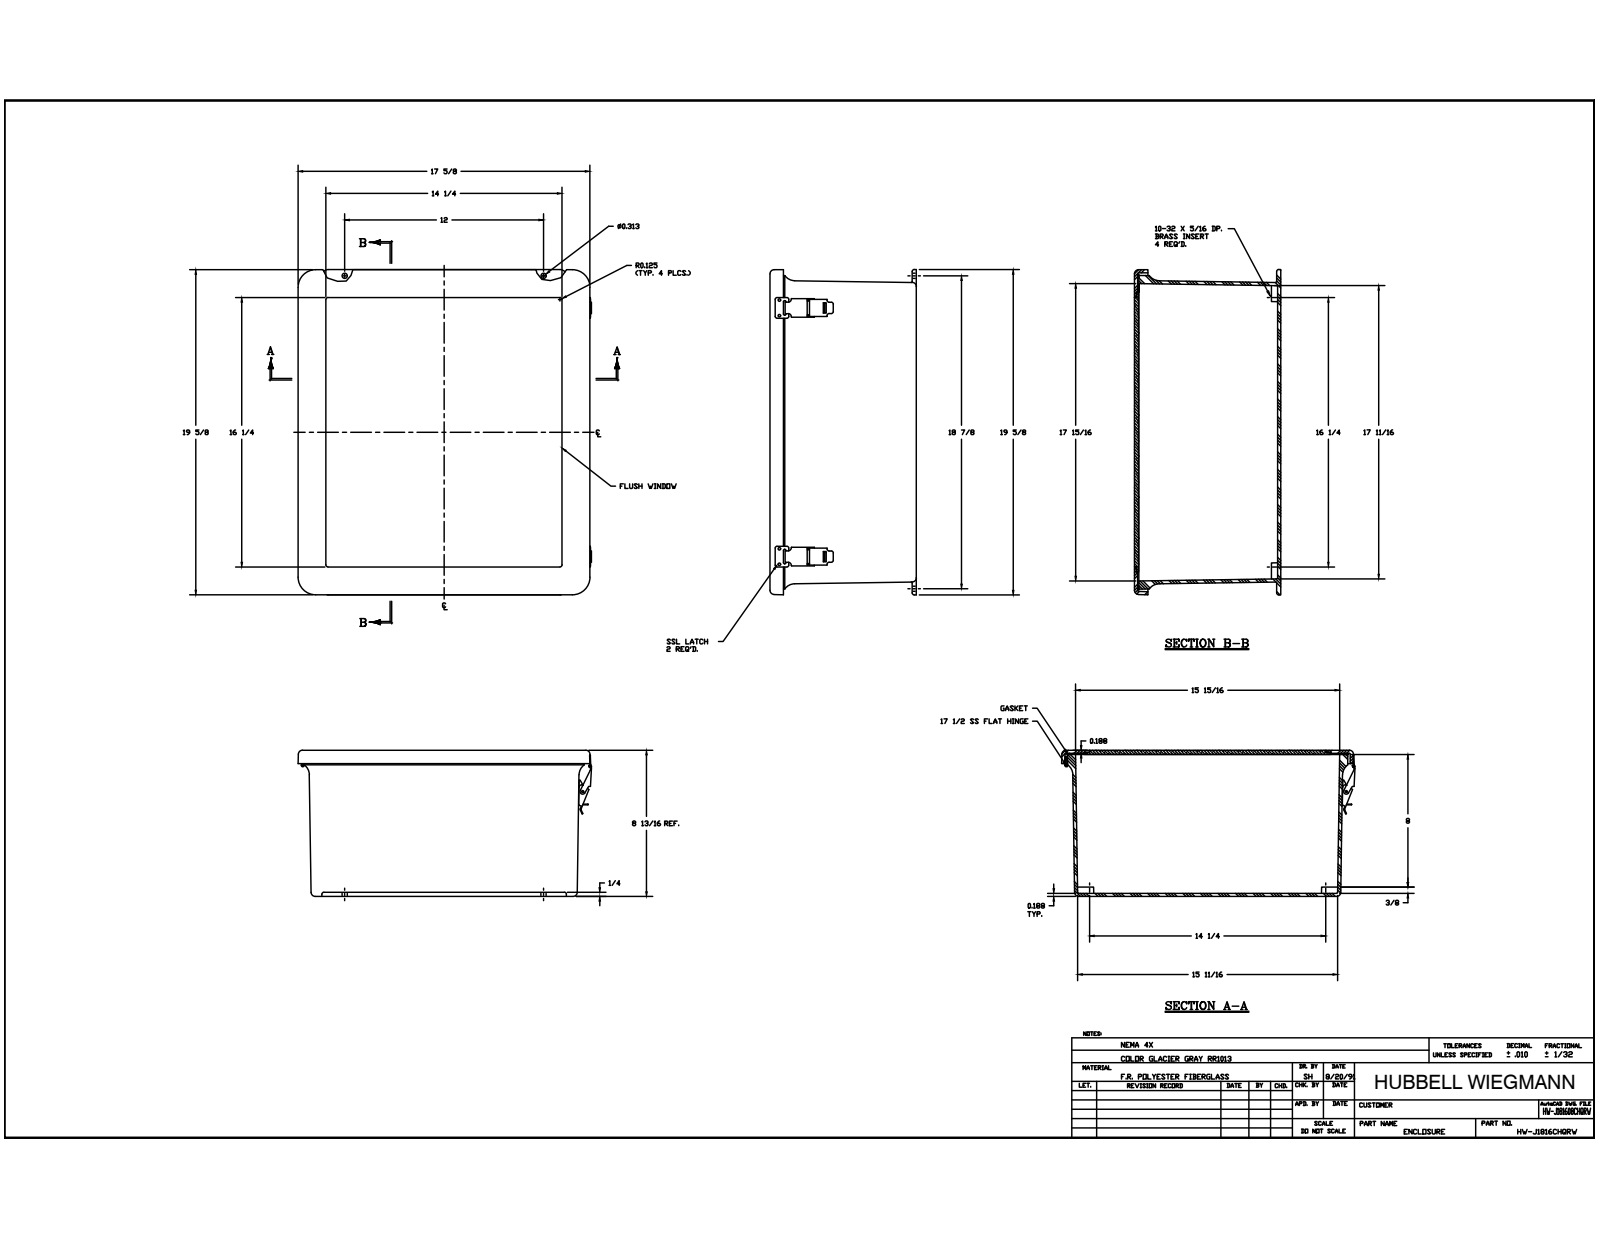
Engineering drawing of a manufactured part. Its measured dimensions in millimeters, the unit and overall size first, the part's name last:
Units: millimetres
Overall size (bounding box): 498.48 × 449.74 × 223.82
Round holes (diameter × count): ⌀3.56 ×24, ⌀3.33 ×12, ⌀2.64 ×8, ⌀3.86 ×5, ⌀3.3 ×4, ⌀3.96 ×4, ⌀5.54 ×4, ⌀3.43 ×2, ⌀9.52 ×2, ⌀2.16 ×1, ⌀2.16 ×1
Round bosses / shafts (diameter × count): ⌀3.17 ×20, ⌀6.35 ×12, ⌀6.86 ×4, ⌀7.62 ×1, ⌀4.31 ×1, ⌀3.94 ×1, ⌀3.05 ×1
Partial cylindrical surfaces — rounded edges, fillets, slot ends (radius × count): R3.17 ×24, R0.38 ×20, R0.79 ×20, R1.14 ×16, R0.76 ×12, R6.35 ×12, R0.57 ×9, R1.52 ×6
Main face-to-face distances: 4.76, 223.82, 4.77, 6.35, 217.47, 219.05, 212.7, 219.06, 214.29, 1.59
Hole centre spacings: 85.72, 85.73, 171.45, 6.36, 380.59, 247.65, 260.35, 380.6
Volume: 4 522 000 mm³ · Surface area: 1 804 000 mm²
Bodies: 43 solids, 1160 faces (524 planar, 485 cylindrical, 151 other)
Part name (STEP PRODUCT): J1816HL_4; RMINS45821P_117; RMINS45821P_118; RMINS45821P_119 (+8 more)
STEP written by: Autodesk Inventor 2014 (AUTOMOTIVE_DESIGN)
